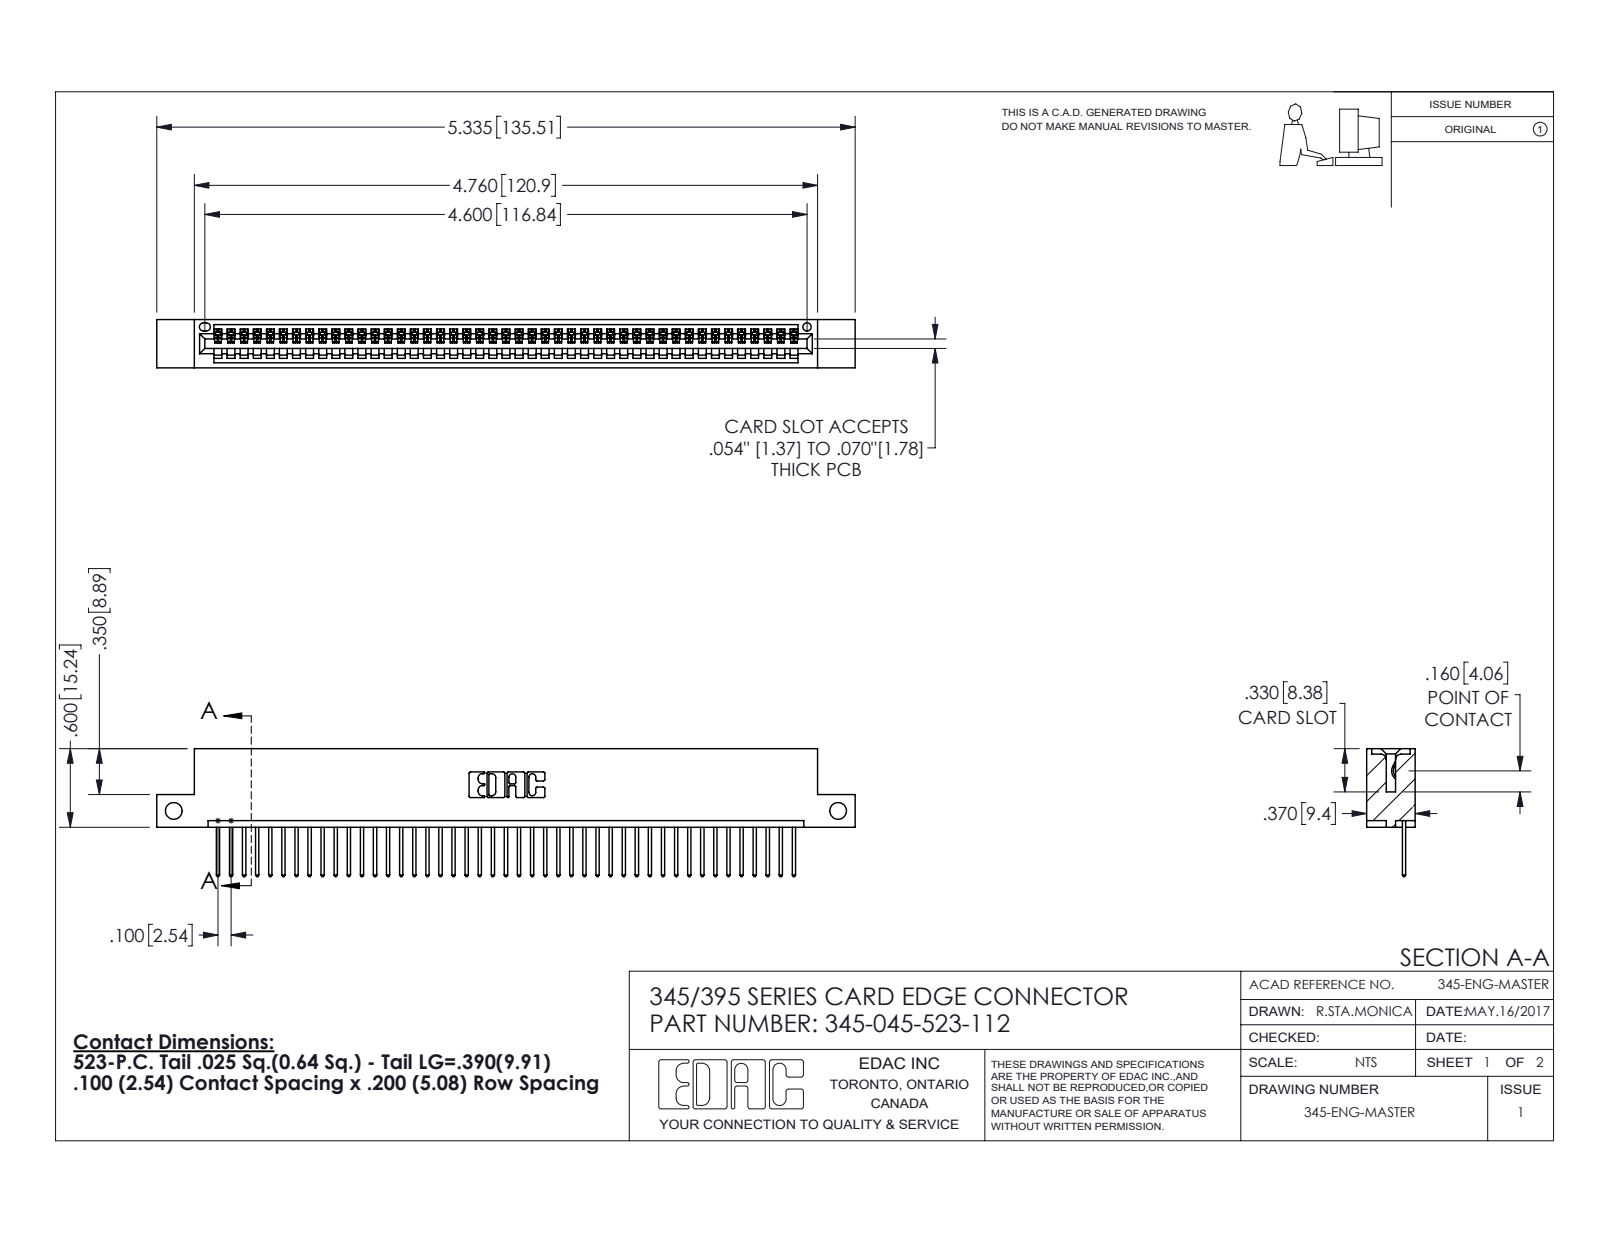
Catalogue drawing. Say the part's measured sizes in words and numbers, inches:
The part is named "345-045-523-112; 345 Part_Flush Mounting Lugs - Side Mount; 345-292-001_345-293-123". Its 3-D file was written by "SolidWorks 2016 (CONFIG_CONTROL_DESIGN)". It is 46 solids with 2736 faces: 1880 planar, 856 cylindrical and 0 other. Overall it measures 5.335 by 0.977 by 0.37 inches. Its volume is 0.781 cubic inches and its surface area 26.27 square inches. Round holes: 2 of diameter 0.128, 1 of diameter 0.064. Partial cylindrical surfaces (rounded edges, fillets, slot ends): 90 of radius 0.006, 90 of radius 0.01, 22 of radius 0.01, 6 of radius 0.007, 6 of radius 0.031, 3 of radius 0.026, 2 of radius 0.031, 2 of radius 0.04. The main face-to-face distances are 0.298, 0.072, 0.37, 0.2, 0.098, 0.272, 0.025, 0.225, 0.149, 0.072. The hole center spacings are 5.075.
